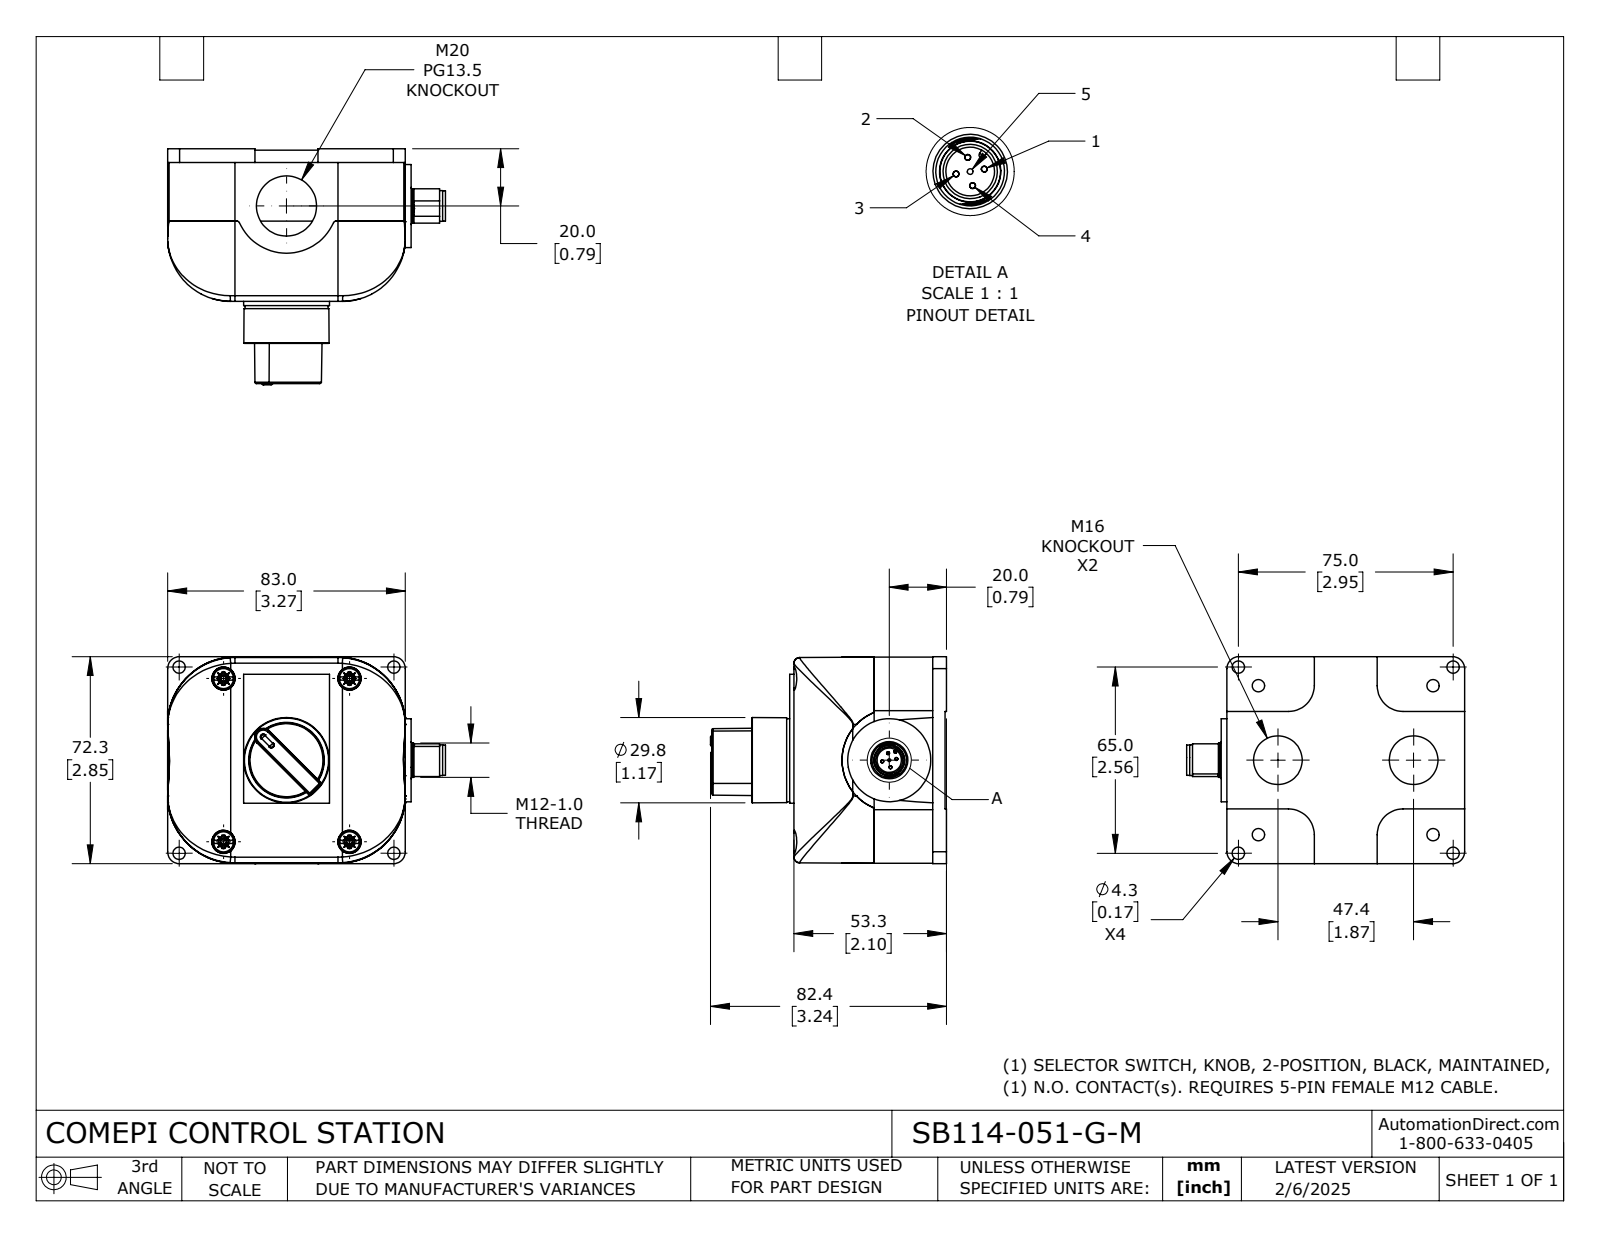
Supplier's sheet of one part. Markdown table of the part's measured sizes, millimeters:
| quantity | value |
| --- | --- |
| part name | SB114-051-G-M |
| STEP written by | SolidWorks 2024 (CONFIG_CONTROL_DESIGN) |
| units | millimeters |
| bodies | 11 solids, 824 faces (402 planar, 288 cylindrical, 134 other) |
| overall size | 97.1 × 82.4 × 72.3 |
| volume | 221 700 mm³ |
| surface area | 65 030 mm² |
| round holes (diameter × count) | 4.3 × 8, 1 × 4, 1.7 × 4, 2.2 × 4, 8.2 × 4, 17 × 2, 21 × 2, 2.5 × 1, 8.5 × 1, 12.7 × 1, 14 × 1, 19.1 × 1 |
| round bosses / shafts (diameter × count) | 1 × 5, 7 × 4, 2.2 × 4, 1.7 × 4, 29 × 2, 0.6 × 2, 26.4 × 1, 25.5 × 1 |
| partial cylindrical surfaces (radius × count) | 0.5 × 8, 1 × 5, 0.9 × 4, 2 × 4, 9 × 4, 9.7 × 4, 23.5 × 4, 0.3 × 2 |
| main face-to-face distances | 52.8, 2.5, 24.8, 28, 22.3, 50.3, 3, 0.5, 25.3, 53.3 |
| hole center spacings | 9.6, 26.9, 35.3, 40.1, 49.6, 58.9, 60.1, 68.3 |
